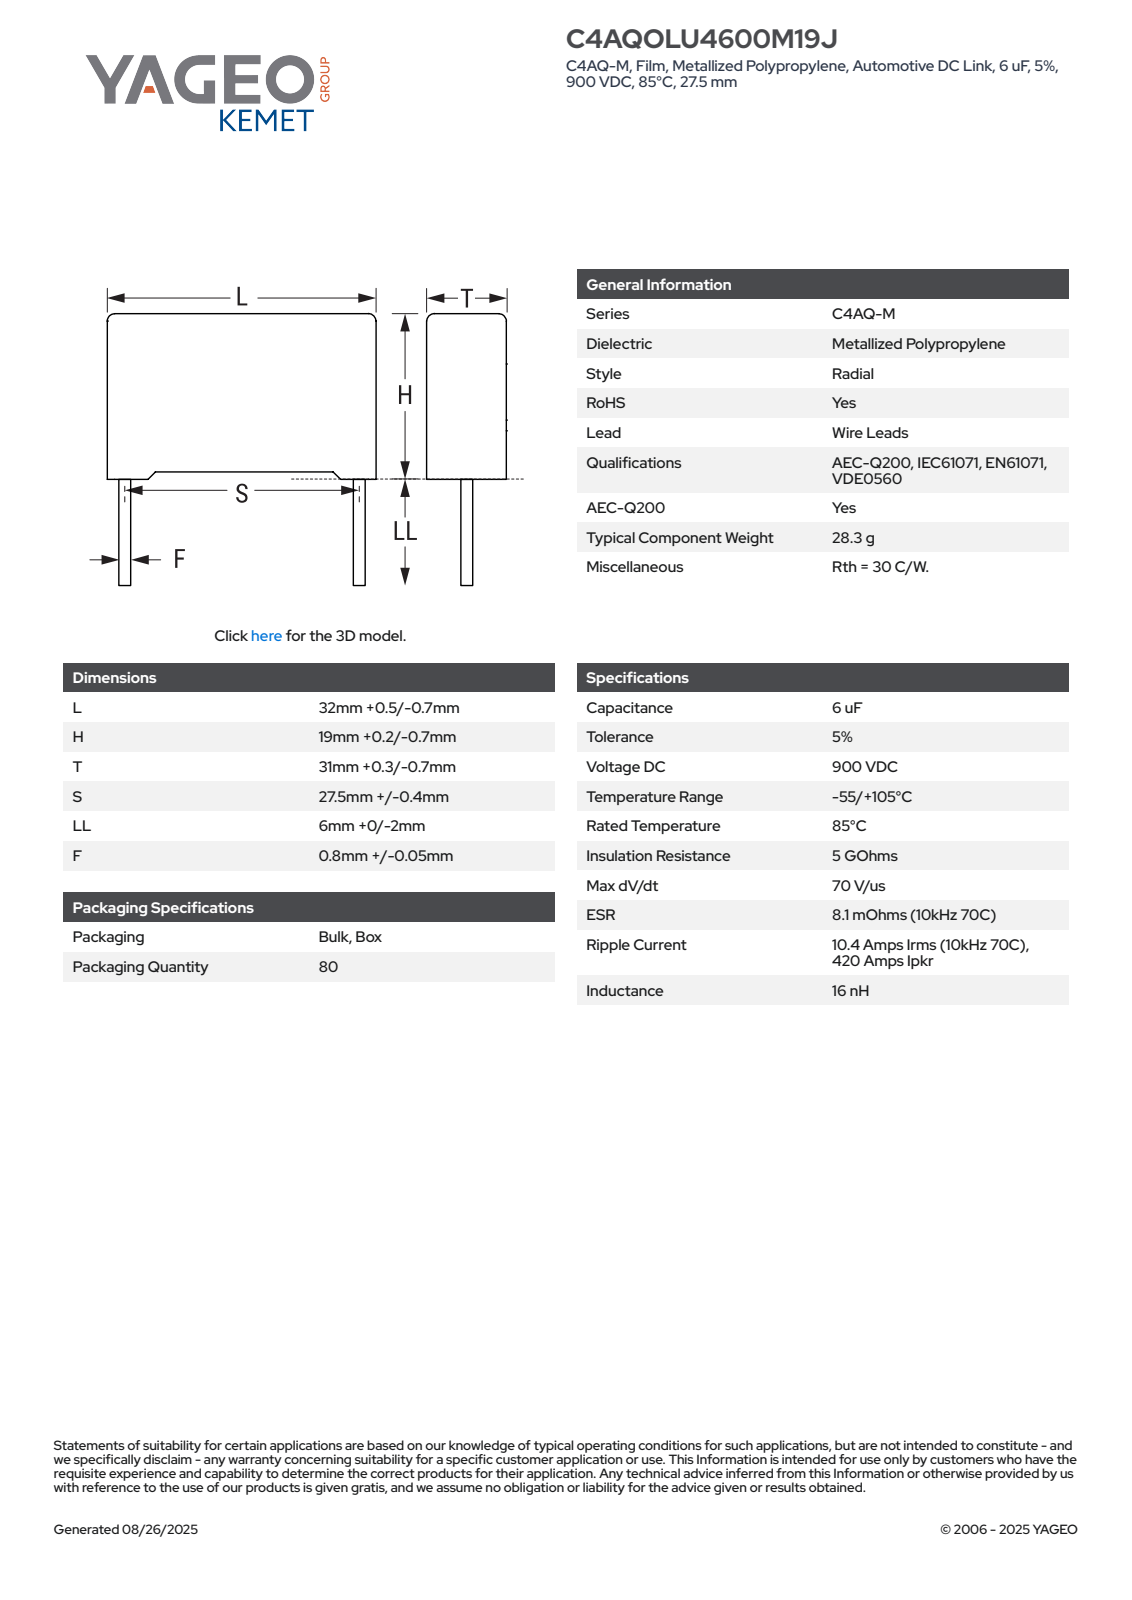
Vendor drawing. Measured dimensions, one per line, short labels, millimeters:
name: CFR_RB2CFP_32X19X31_L32.5H19.2T31.3S27.5LL6F0.85
written by: SolidWorks 2014 (AUTOMOTIVE_DESIGN)
unit: mm
bodies: 4 solids, 85 faces (77 planar, 8 cylindrical, 0 other)
size: 32.5 × 31.3 × 25.2
volume: 18 836 mm³; area: 4 600 mm²
bosses: 2× ⌀0.85
rounds: 4× R0.5
face distances: 18.45, 31.3, 32.5, 0.75, 19.2, 1.08, 0.66, 18.54, 31.42, 30.34
